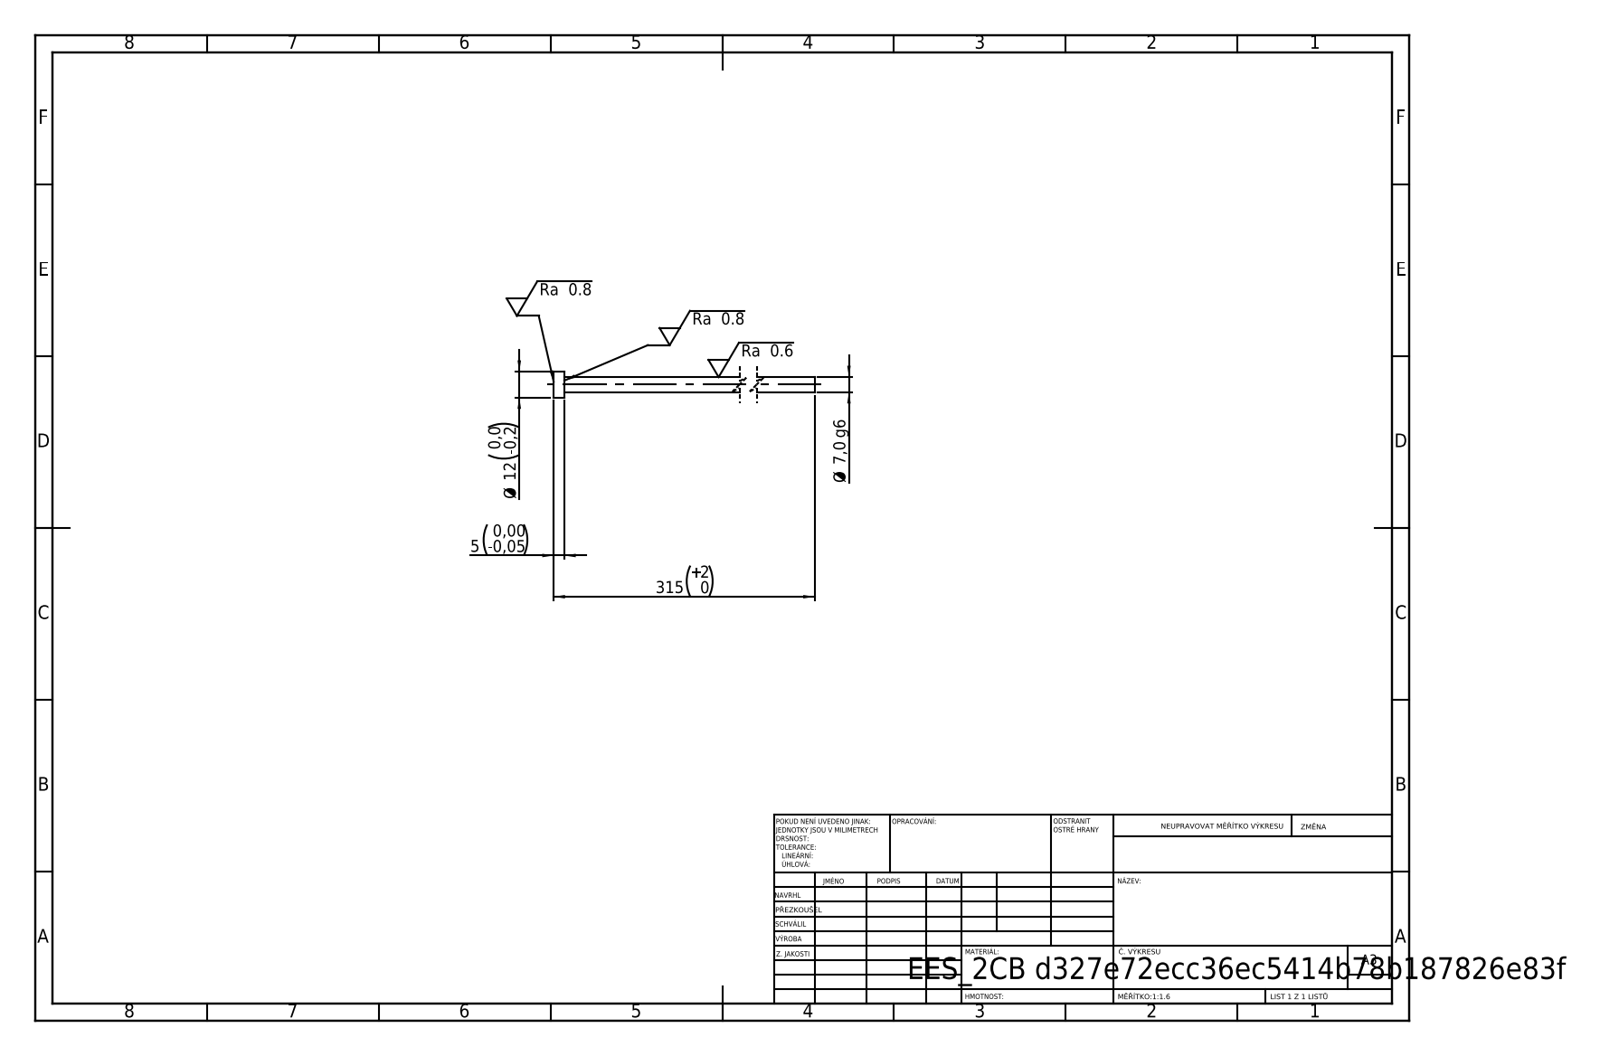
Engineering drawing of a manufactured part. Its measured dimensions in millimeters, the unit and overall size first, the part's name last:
Units: millimetres
Overall size (bounding box): 315 × 12 × 12
Round bosses / shafts (diameter × count): ⌀12 ×1, ⌀7 ×1
Main face-to-face distances: 5, 315, 310
Volume: 12 496 mm³ · Surface area: 7 232 mm²
Bodies: 1 solid, 7 faces (3 planar, 4 cylindrical, 0 other)
STEP written by: SolidWorks 2019 (CONFIG_CONTROL_DESIGN)
